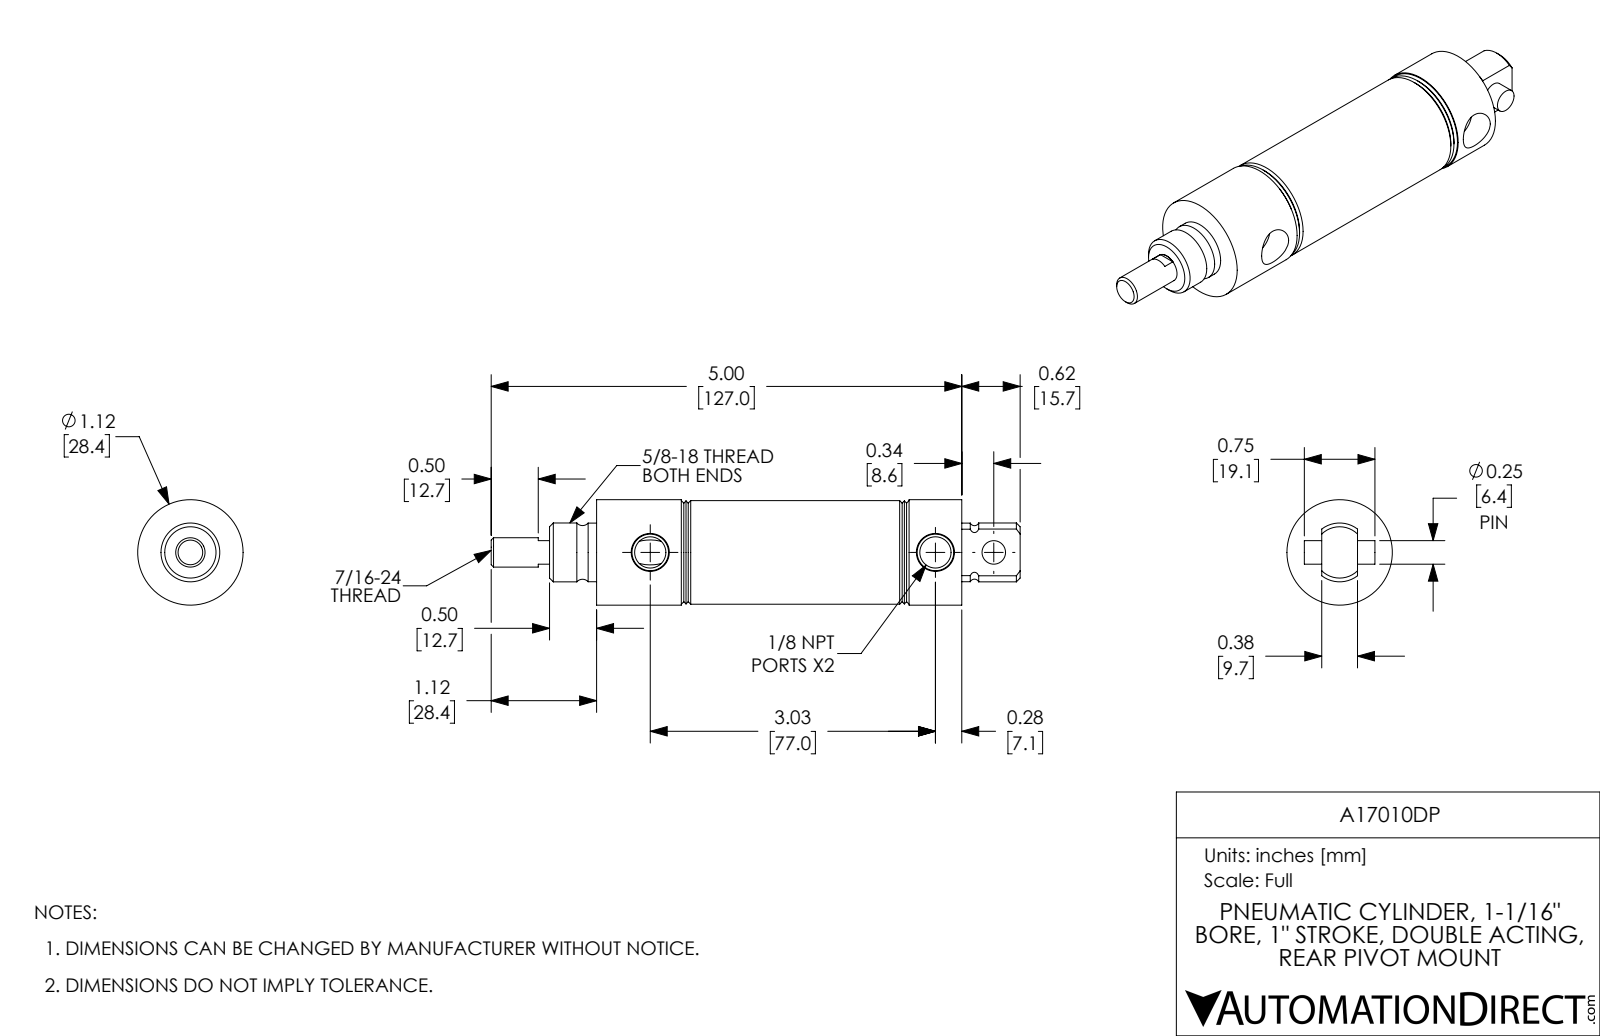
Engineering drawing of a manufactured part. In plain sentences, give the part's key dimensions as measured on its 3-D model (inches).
The part is named "A17010DP; A17010DP-PIN; A17010DP-Rod; A17010DP-MainBody". Its 3-D file was written by "SolidWorks 2017 (AUTOMOTIVE_DESIGN)". It is 3 solids with 91 faces: 23 planar, 30 cylindrical and 38 other. Overall it measures 5.62 by 1.12 by 1.12 inches. Its volume is 3.168 cubic inches and its surface area 34.55 square inches. Round holes: 2 of diameter 0.332, 1 of diameter 0.25, 1 of diameter 0.312, 1 of diameter 1.063. Round bosses or shafts: 1 of diameter 1.12, 1 of diameter 1.1, 1 of diameter 0.625, 1 of diameter 0.623. Partial cylindrical surfaces (rounded edges, fillets, slot ends): 1 of radius 0.313. The main face-to-face distances are 0.5, 2.69, 1.5, 1, 1.19, 1.69, 2.69, 3.88, 2.19, 1.19. The hole center spacings are 0.62, 3.03, 3.65.
